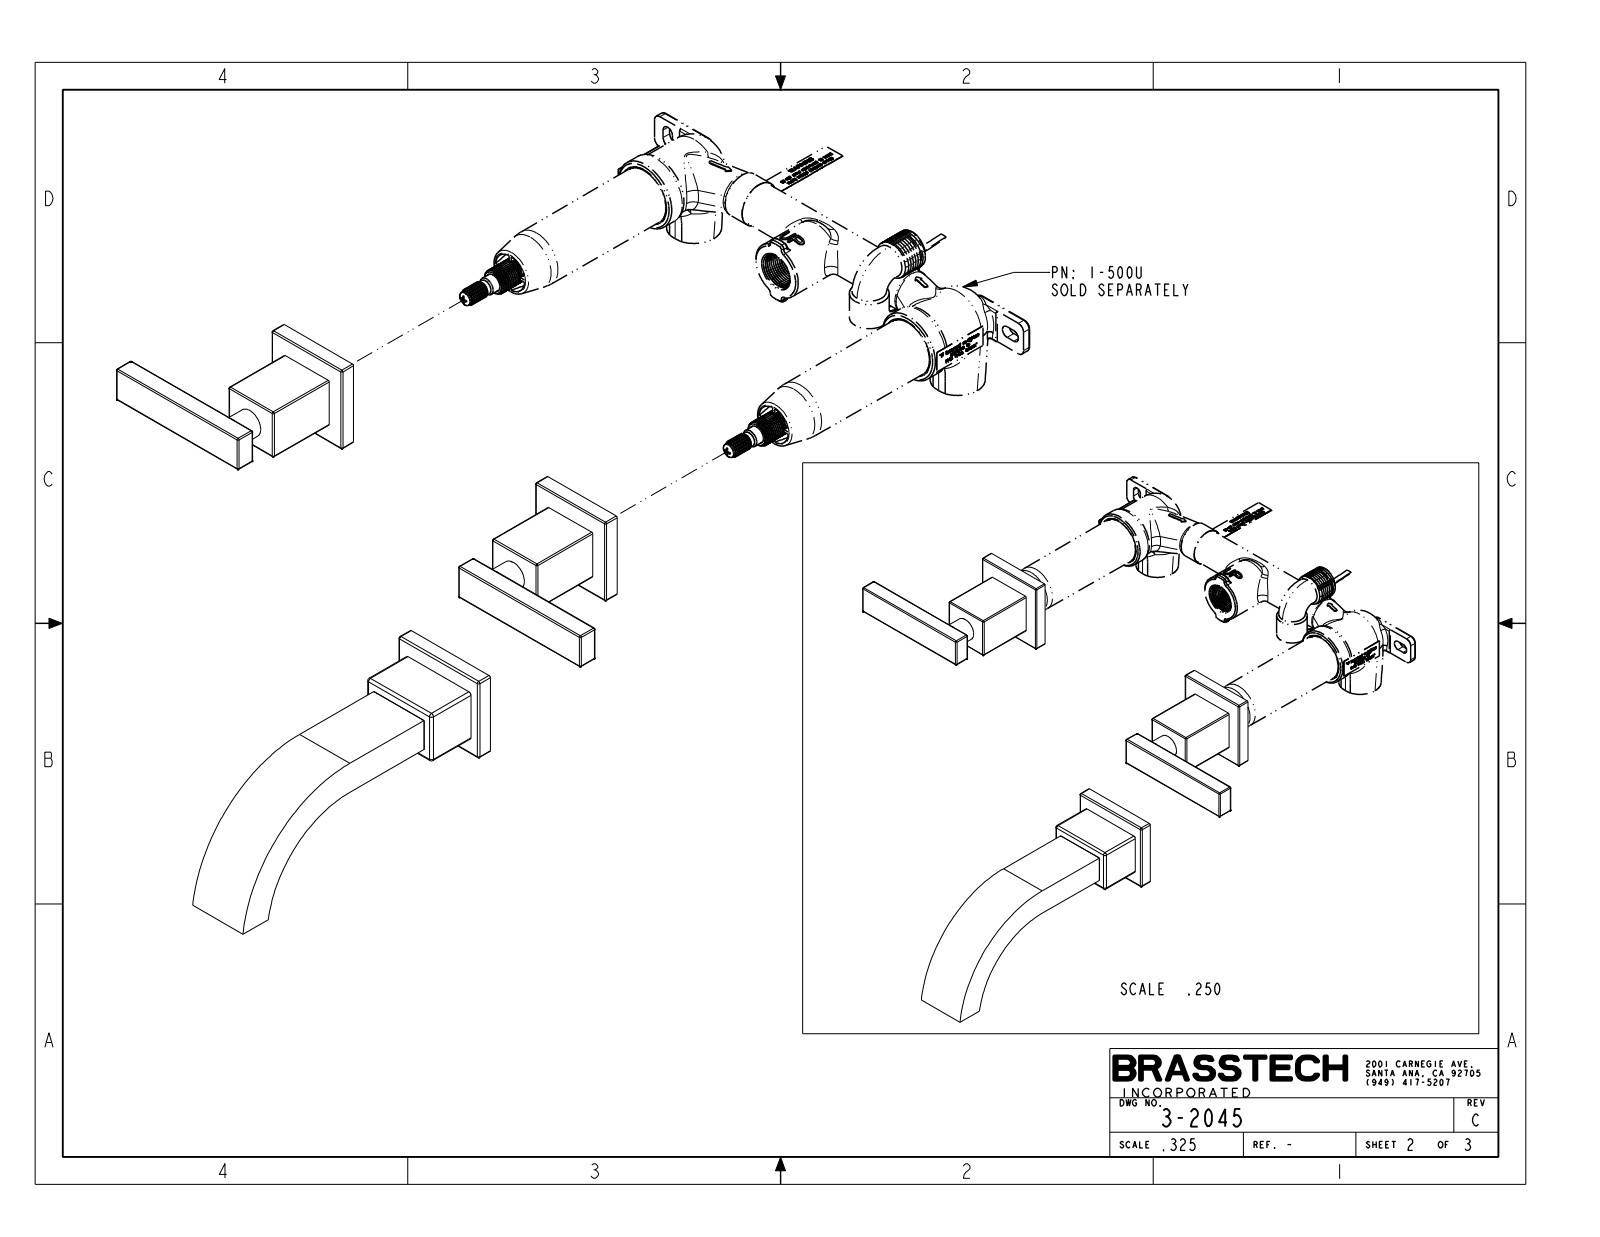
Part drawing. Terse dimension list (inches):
name: 3-2045_SW0001
written by: CREO PARAMETRIC BY PTC INC, 2018400 (AUTOMOTIVE_DESIGN)
unit: in
bodies: 3 solids, 188 faces (54 planar, 86 cylindrical, 48 other)
size: 13.875 × 9.47 × 6.94
volume: 22.69 in³; area: 107.4 in²
bosses: 2× ⌀0.65, 2× ⌀0.523
rounds: 48× R0.03, 8× R0.04, 8× R0.06, 1× R2.463, 1× R3.213
face distances: 0.35, 0.18, 0.98, 0.45, 3.05, 2.7, 1.5, 2.6, 2.25, 1.72
